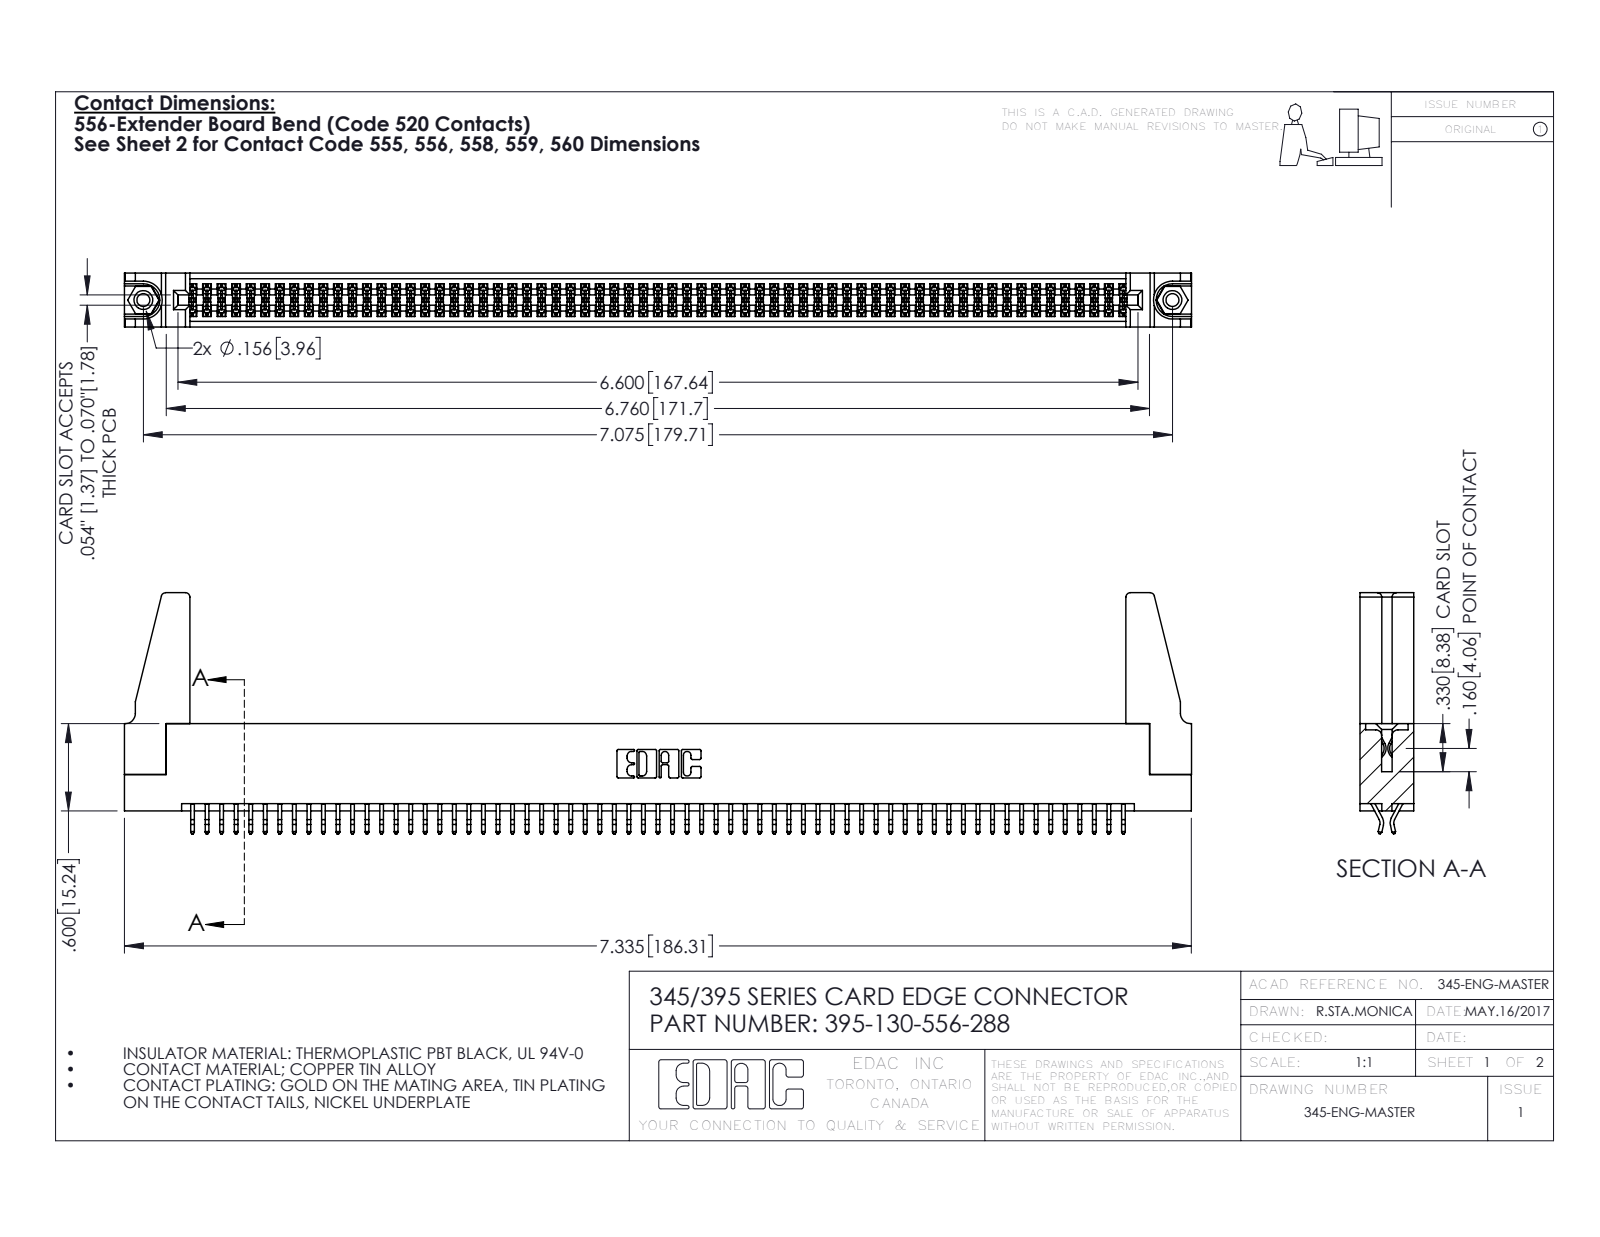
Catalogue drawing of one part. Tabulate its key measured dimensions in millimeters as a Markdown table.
| quantity | value |
| --- | --- |
| part name | 395-130-556-288; 345-250-001_345-250-001-102; 345-292-001_556 Tail; 345-220-078_345-220-088 (+1 more) |
| STEP written by | SolidWorks 2016 (CONFIG_CONTROL_DESIGN) |
| units | millimeters |
| bodies | 135 solids, 7530 faces (4962 planar, 2552 cylindrical, 16 other) |
| overall size | 186.3 × 42.1 × 9.4 |
| volume | 21 570 mm³ |
| surface area | 30 520 mm² |
| round holes (diameter × count) | 2.3 × 2, 3.2 × 2, 4 × 2, 1.6 × 1 |
| round bosses / shafts (diameter × count) | 3.9 × 2 |
| partial cylindrical surfaces (radius × count) | 0.2 × 195, 0.3 × 22, 0.8 × 8, 0.2 × 6, 0.8 × 6, 0.7 × 3, 0.3 × 2, 0.4 × 2 |
| main face-to-face distances | 1.8, 7.6, 9.4, 5.1, 0.6, 2.5, 6.9, 5.7, 4.4, 3.8 |
| hole center spacings | 6.9, 173.7, 179.7 |
